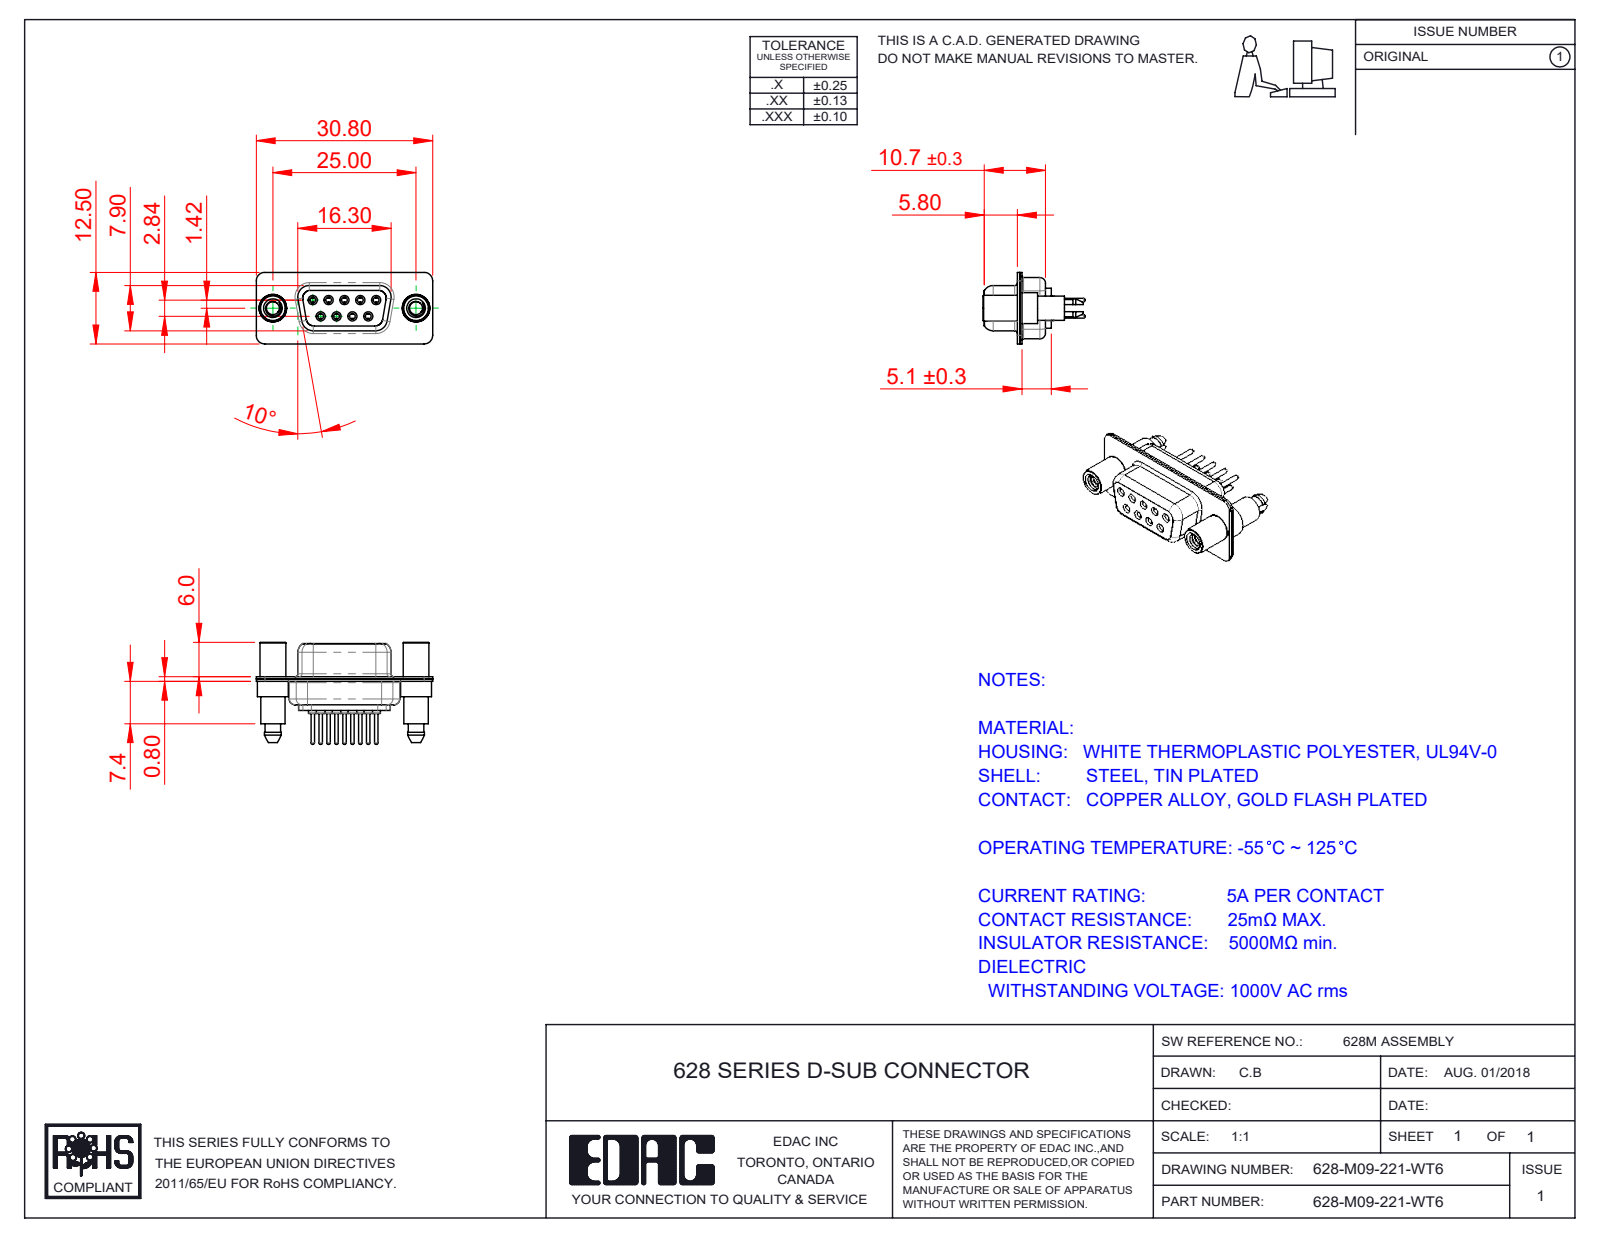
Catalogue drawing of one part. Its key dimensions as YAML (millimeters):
part_name: "628M Contact Row 1_21; 628M Contact Row 2_21; 628M Shell Front_09 Contacts; 628-M09-221-WT6 (+3 more)"
step_written_by: "SolidWorks 2020 (CONFIG_CONTROL_DESIGN)"
units: millimeters
bodies: {solids: 14, faces: 826, planar: 220, cylindrical: 336, other: 270}
overall_size: [30.8, 17.8, 12.5]
volume: 2041
surface_area: 4890
round_holes:
  - {diameter: 1, count: 9}
  - {diameter: 1.1, count: 9}
  - {diameter: 1.7, count: 9}
  - {diameter: 1.8, count: 9}
  - {diameter: 2, count: 9}
  - {diameter: 2.26, count: 2}
  - {diameter: 4, count: 2}
  - {diameter: 4.8, count: 2}
round_bosses_or_shafts:
  - {diameter: 2.2, count: 9}
  - {diameter: 1.6, count: 9}
  - {diameter: 1.5, count: 9}
  - {diameter: 0.6, count: 9}
  - {diameter: 5.4, count: 2}
  - {diameter: 4.9, count: 2}
  - {diameter: 4.5, count: 2}
  - {diameter: 4.25, count: 2}
partial_cylinders:
  - {radius: 1.5, count: 18}
  - {radius: 2, count: 12}
  - {radius: 1.6, count: 10}
  - {radius: 1.35, count: 8}
  - {radius: 0.25, count: 4}
  - {radius: 0.5, count: 4}
  - {radius: 0.6, count: 4}
  - {radius: 0.65, count: 4}
face_to_face_distances: [0.4, 1.4, 0.45, 8.45, 0.8, 1.8, 1, 8.9, 6.2, 9.3]
hole_center_spacings: [3.16, 2.77, 5.54, 5.03, 5.04, 8.31, 7.1, 7.48]
